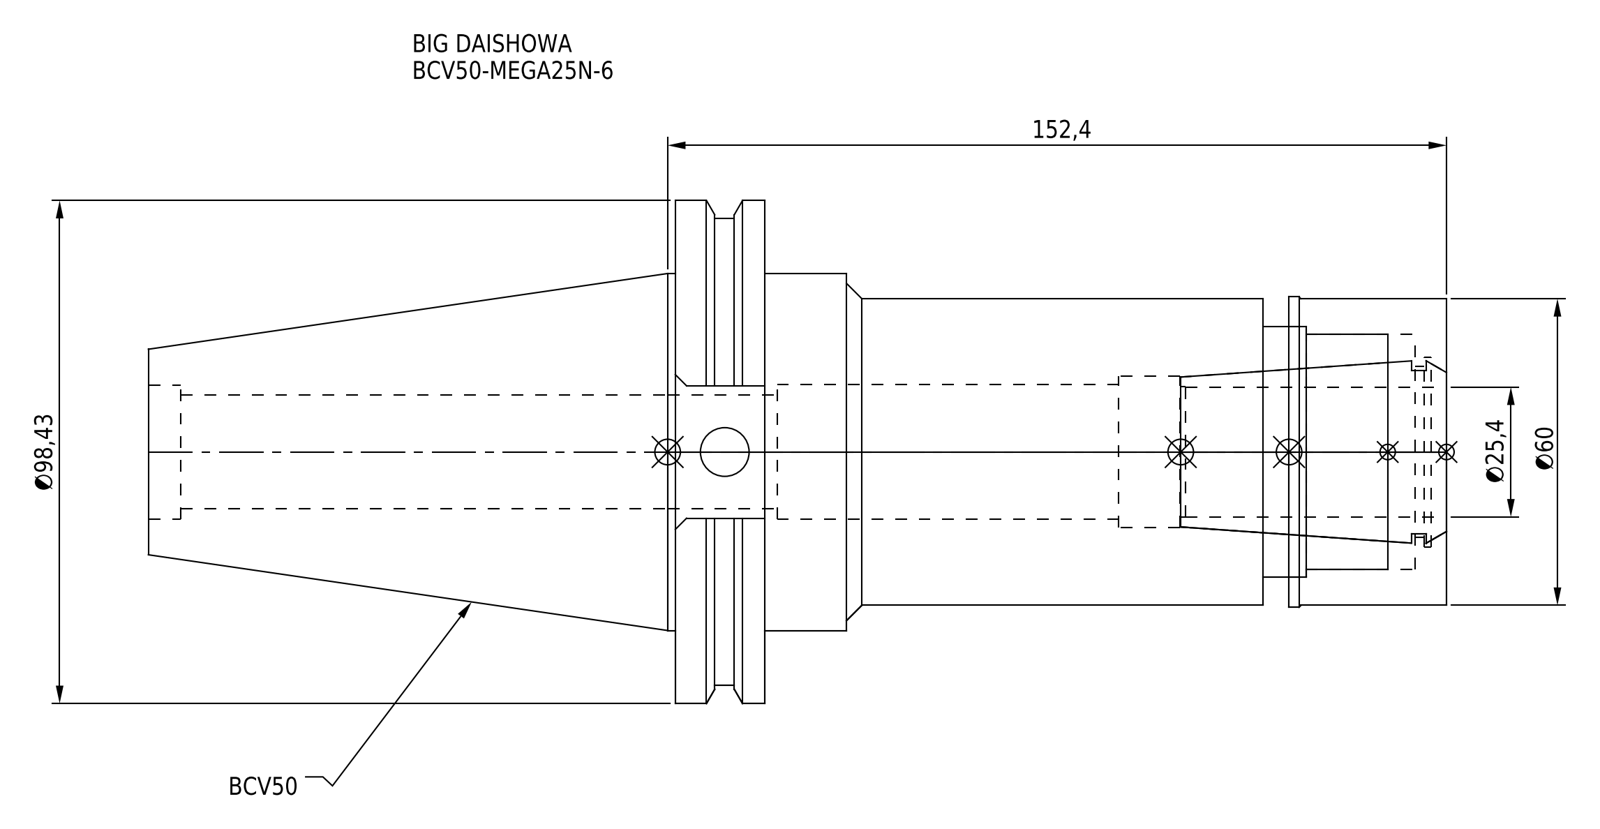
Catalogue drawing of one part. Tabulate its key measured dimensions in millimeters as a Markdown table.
| quantity | value |
| --- | --- |
| part name | BCV50-MEGA25N-6_1.stp; BCV50MN25060-254_ASM.stp; BCV50-MEGA25N-6; DXF_TEMP_ASSY_ASM_4_ASM.stp (+3 more) |
| STEP written by | SolidWorks 2019 (CONFIG_CONTROL_DESIGN) |
| units | millimeters |
| bodies | 2 solids, 86 faces (32 planar, 40 cylindrical, 14 other) |
| overall size | 254 × 98.42 × 94.95 |
| volume | 619 260 mm³ |
| surface area | 91 722 mm² |
| round holes (diameter × count) | 9.53 × 1, 22.3 × 1, 26.23 × 1, 26.3 × 1, 29.6 × 1, 33.5 × 1, 37.2 × 1, 46 × 1, 49 × 1 |
| round bosses / shafts (diameter × count) | 98.42 × 1, 91.29 × 1, 69.85 × 1, 60.7 × 1, 60 × 1 |
| main face-to-face distances | 17.55, 133.35, 150.9, 30.8, 102.55, 120.1, 35.9, 5.1, 97.45, 115 |
